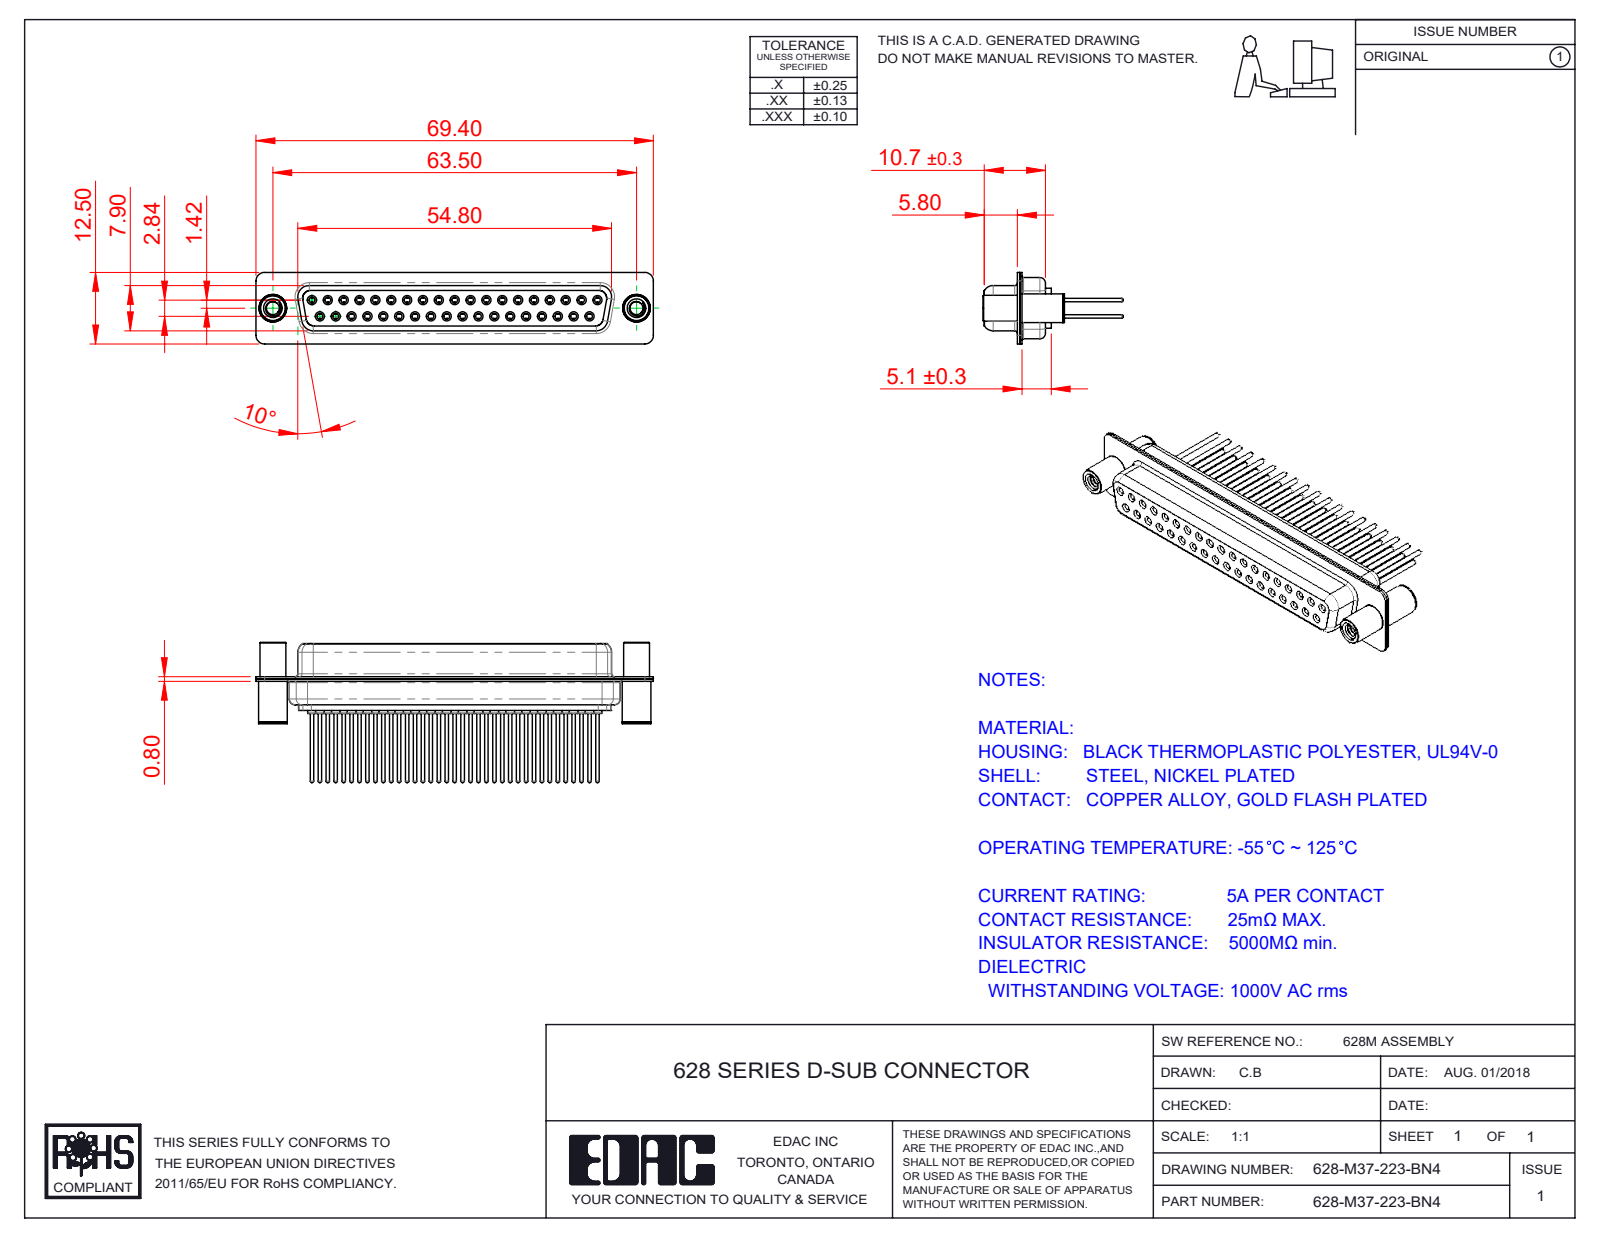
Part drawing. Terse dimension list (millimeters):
name: 628M Contact Row 2_23; 628M Contact Row 1_23; 628M Shell Front_37 Contacts; 628-M37-223-BN4 (+3 more)
written by: SolidWorks 2020 (CONFIG_CONTROL_DESIGN)
unit: mm
bodies: 42 solids, 2400 faces (628 planar, 892 cylindrical, 880 other)
size: 69.4 × 24.47 × 12.5
volume: 5 610 mm³; area: 13 660 mm²
holes: 37× ⌀1, 37× ⌀1.1, 37× ⌀1.7, 37× ⌀1.8, 37× ⌀2, 2× ⌀2.26, 2× ⌀3.26, 2× ⌀4, 2× ⌀4.8
bosses: 37× ⌀2.2, 37× ⌀1.6, 37× ⌀1.5, 37× ⌀0.6, 2× ⌀5, 2× ⌀4.9, 2× ⌀4.5
rounds: 16× R1.5, 12× R2, 8× R1.35, 8× R1.6, 4× R0.25, 4× R0.5, 4× R0.6, 4× R0.65
face distances: 0.4, 1.4, 0.45, 8.45, 8.9, 1.8, 6.2, 7.05, 1, 1.85
hole spacings: 2.77, 5.54, 8.31, 3.16, 11.08, 13.85, 16.62, 19.39
